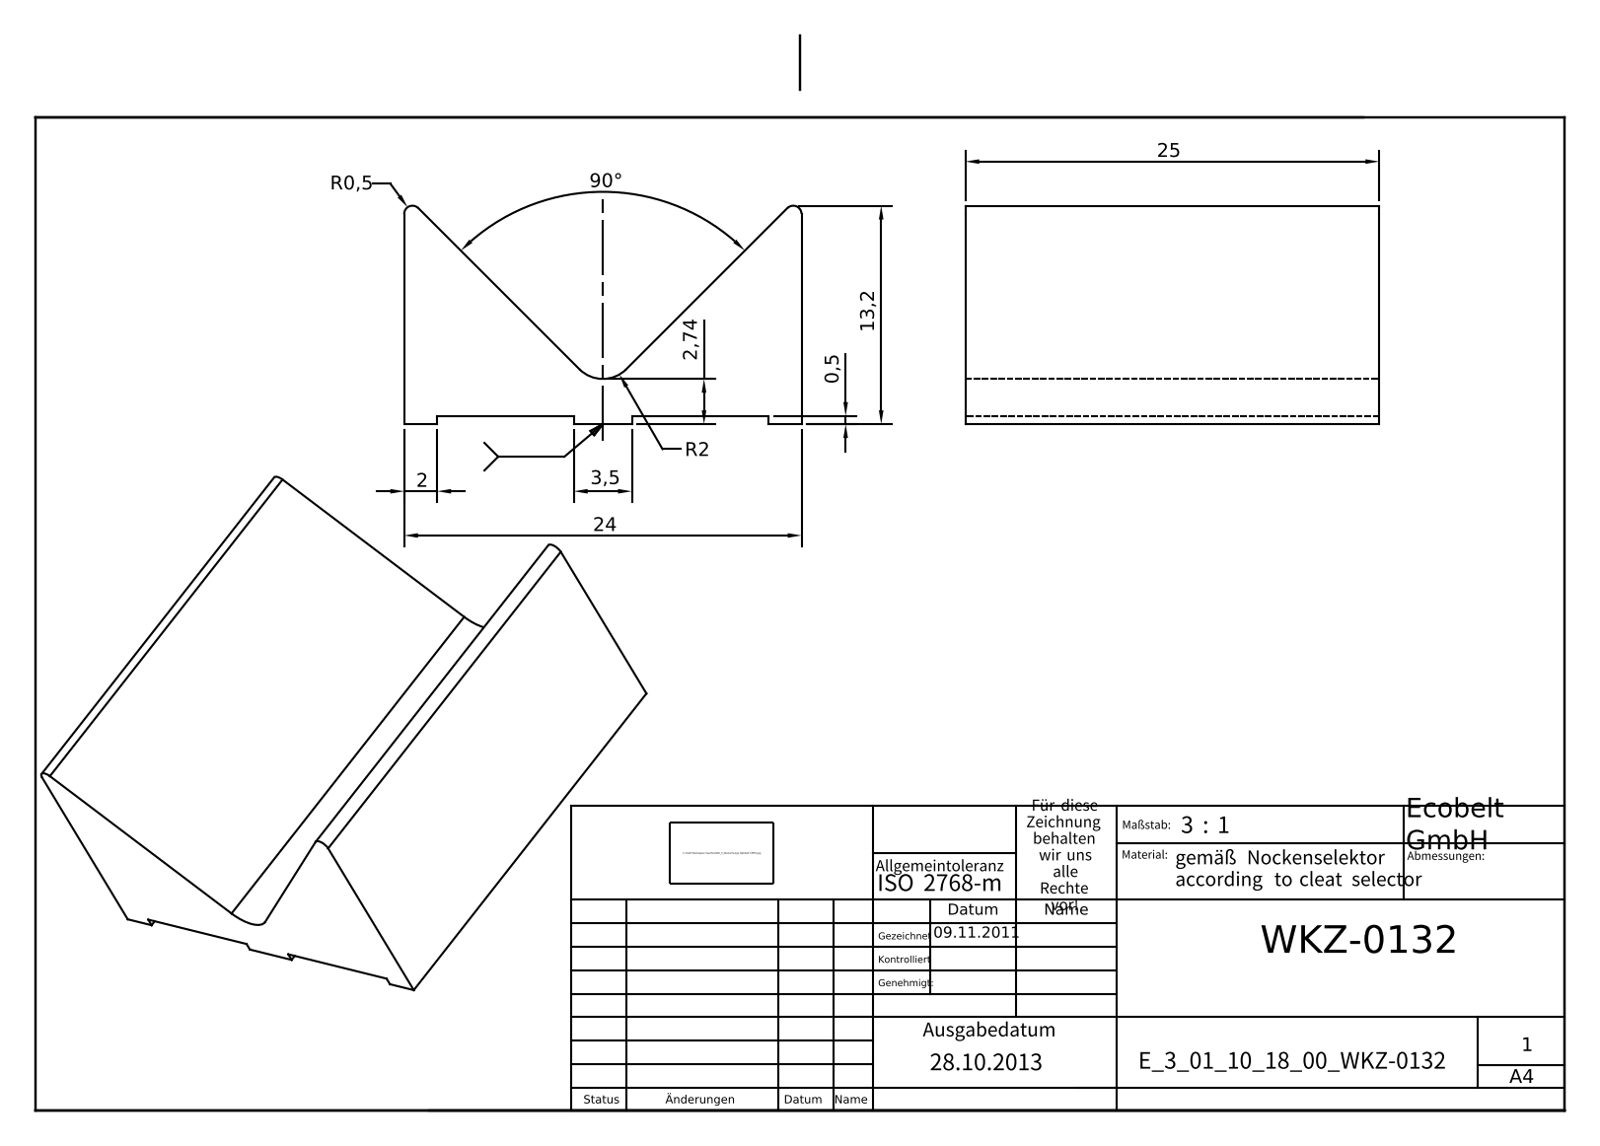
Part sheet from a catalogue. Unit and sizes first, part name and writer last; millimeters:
Units: millimetres
Overall size (bounding box): 25 × 24 × 13.2
Partial cylindrical surfaces — rounded edges, fillets, slot ends (radius × count): R0.5 ×2, R2 ×1
Main face-to-face distances: 24, 0.5, 25, 2, 22, 10.25, 13.75, 8.25, 11.75, 20
Volume: 4 544 mm³ · Surface area: 2 474 mm²
Bodies: 1 solid, 18 faces (15 planar, 3 cylindrical, 0 other)
Part name (STEP PRODUCT): E_3_01_10_18_00_WKZ-0132
STEP written by: Autodesk Inventor 2025 (AUTOMOTIVE_DESIGN)
